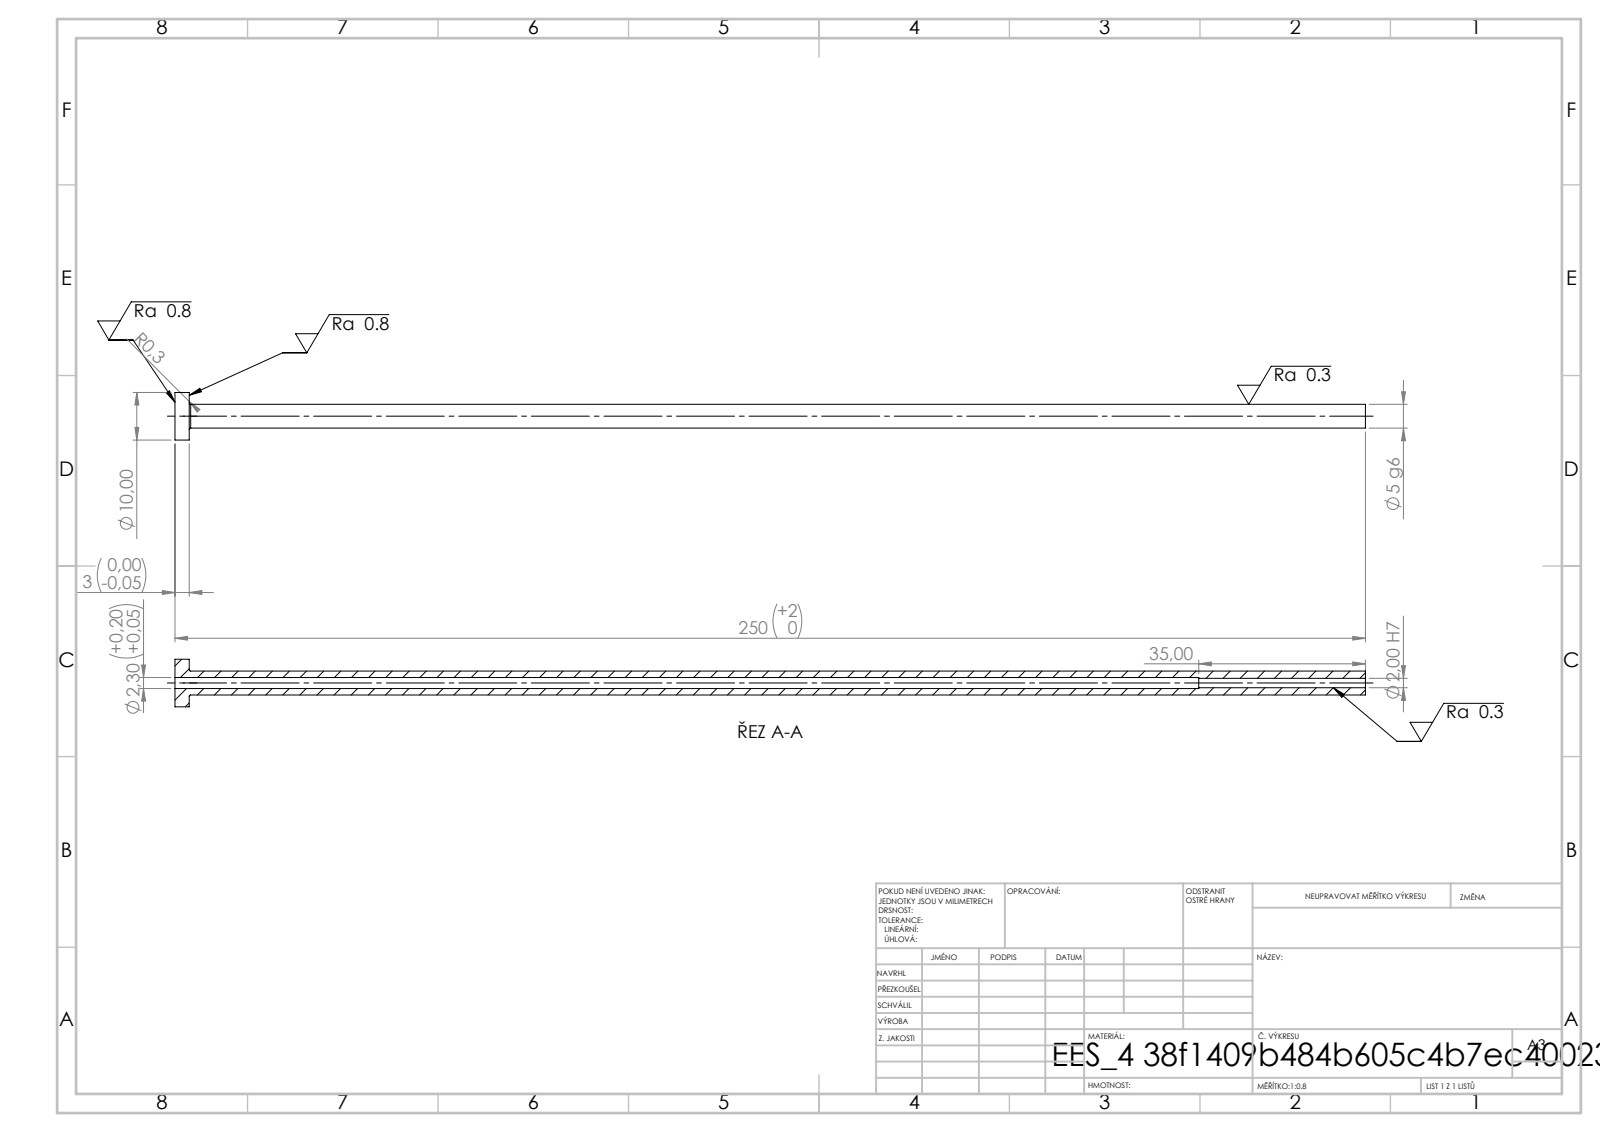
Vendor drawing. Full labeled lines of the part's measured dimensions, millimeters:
STEP written by: SolidWorks 2019 (CONFIG_CONTROL_DESIGN)
Units: millimetres
Bodies: 1 solid, 14 faces (4 planar, 8 cylindrical, 2 other)
Overall size (bounding box): 250 × 10 × 10
Volume: 4 083 mm³ · Surface area: 5 896 mm²
Round holes (diameter × count): ⌀2 ×1, ⌀2.3 ×1
Round bosses / shafts (diameter × count): ⌀10 ×1, ⌀5 ×1
Main face-to-face distances: 3, 250, 247, 215, 212, 35
